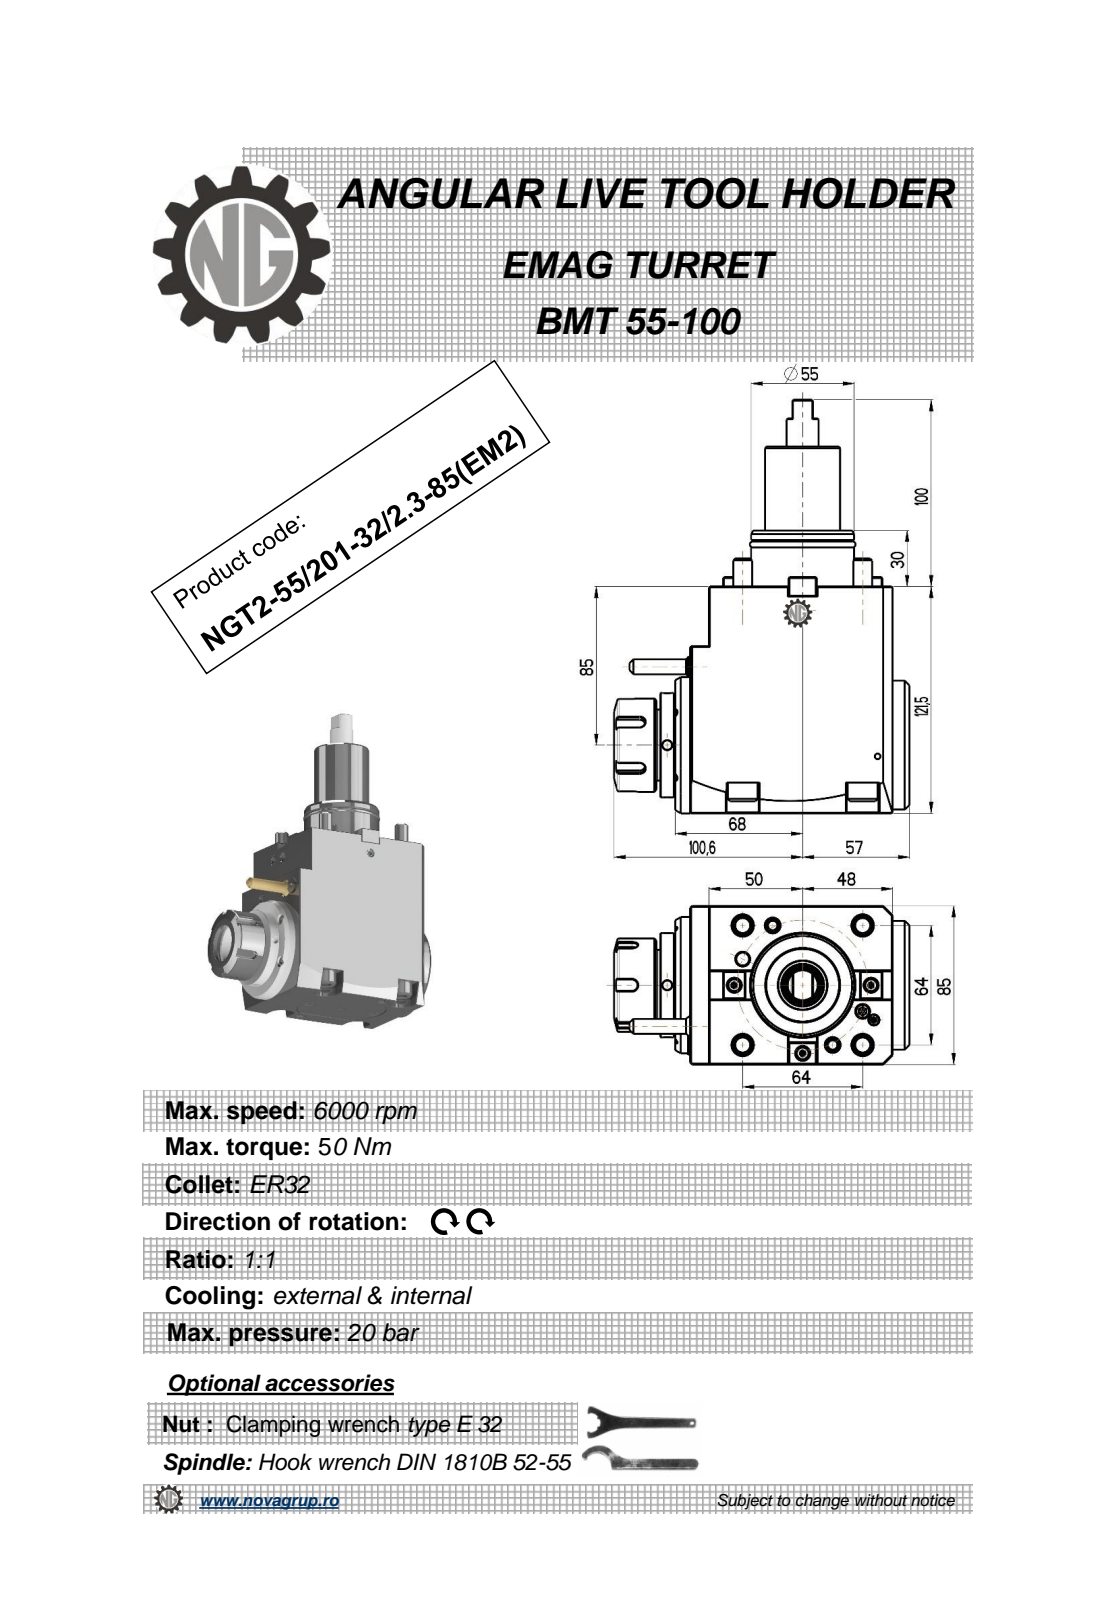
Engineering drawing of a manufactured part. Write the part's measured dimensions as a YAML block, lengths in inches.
part_name: "NGT2_55_201_32_1_3_85_EM2"
step_written_by: "PRO/ENGINEER BY PARAMETRIC TECHNOLOGY CORPORATION, 2010280 (CONFIG_CONTROL_DESIGN)"
units: inches
bodies: {solids: 2, faces: 495, planar: 241, cylindrical: 117, other: 137}
overall_size: [8.72, 6.205, 3.346]
volume: 80.86
surface_area: 178.1
round_holes:
  - {diameter: 0.197, count: 3}
  - {diameter: 0.268, count: 2}
  - {diameter: 0.118, count: 1}
  - {diameter: 0.472, count: 1}
  - {diameter: 1.063, count: 1}
round_bosses_or_shafts:
  - {diameter: 0.63, count: 4}
  - {diameter: 0.394, count: 4}
  - {diameter: 1.969, count: 2}
  - {diameter: 2.874, count: 1}
  - {diameter: 2.717, count: 1}
  - {diameter: 2.205, count: 1}
  - {diameter: 2.165, count: 1}
  - {diameter: 1.709, count: 1}
partial_cylinders:
  - {radius: 0.013, count: 20}
  - {radius: 0.009, count: 6}
  - {radius: 0.012, count: 6}
  - {radius: 0.118, count: 5}
  - {radius: 0.335, count: 4}
  - {radius: 0.031, count: 2}
  - {radius: 18.898, count: 2}
face_to_face_distances: [3.346, 4.783, 0.354, 4.213, 0.315, 0.394, 4.252, 4.606, 0.709, 4.567]
hole_center_spacings: [1.678, 1.867, 2.75, 4.141]
